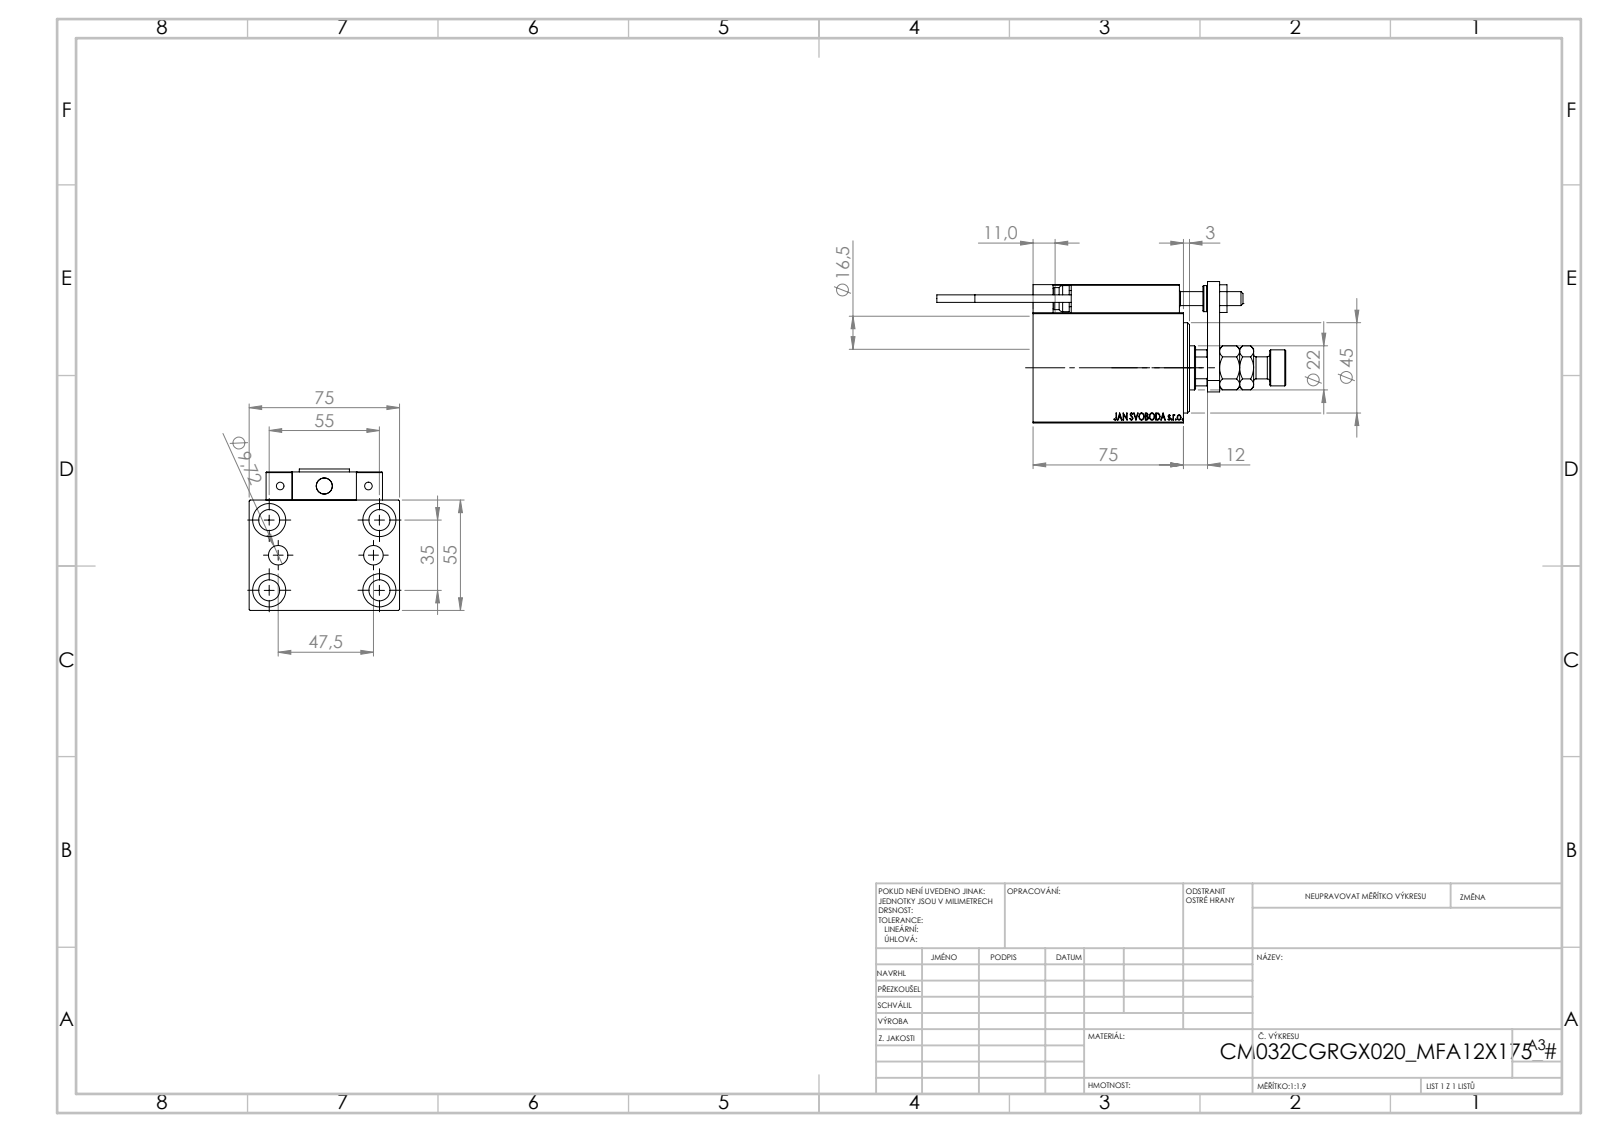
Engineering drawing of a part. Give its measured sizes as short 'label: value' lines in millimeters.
name: ALLEN BOLT D5; V450CM_VC_B; Block; V450CM_C_VCP (+8 more)
written by: SolidWorks 2019 (CONFIG_CONTROL_DESIGN)
unit: mm
bodies: 24 solids, 1330 faces (576 planar, 188 cylindrical, 566 other)
size: 174 × 75 × 70.5
volume: 322 071 mm³; area: 89 964 mm²
holes: 6× ⌀4, 5× ⌀8, 5× ⌀10.5, 5× ⌀16.5, 4× ⌀3.2, 2× ⌀5, 2× ⌀9.72, 1× ⌀7, 1× ⌀22, 1× ⌀25.5, 1× ⌀32, 1× ⌀34
bosses: 2× ⌀11, 2× ⌀5, 2× ⌀3.8, 1× ⌀18, 1× ⌀13
rounds: 30× R0.3, 2× R3, 1× R10.5
face distances: 55, 75, 14, 10, 3, 69, 23, 18, 20, 25
hole spacings: 17.9, 32.6, 54.16, 11.37, 20, 23.75, 27.07, 29.59
